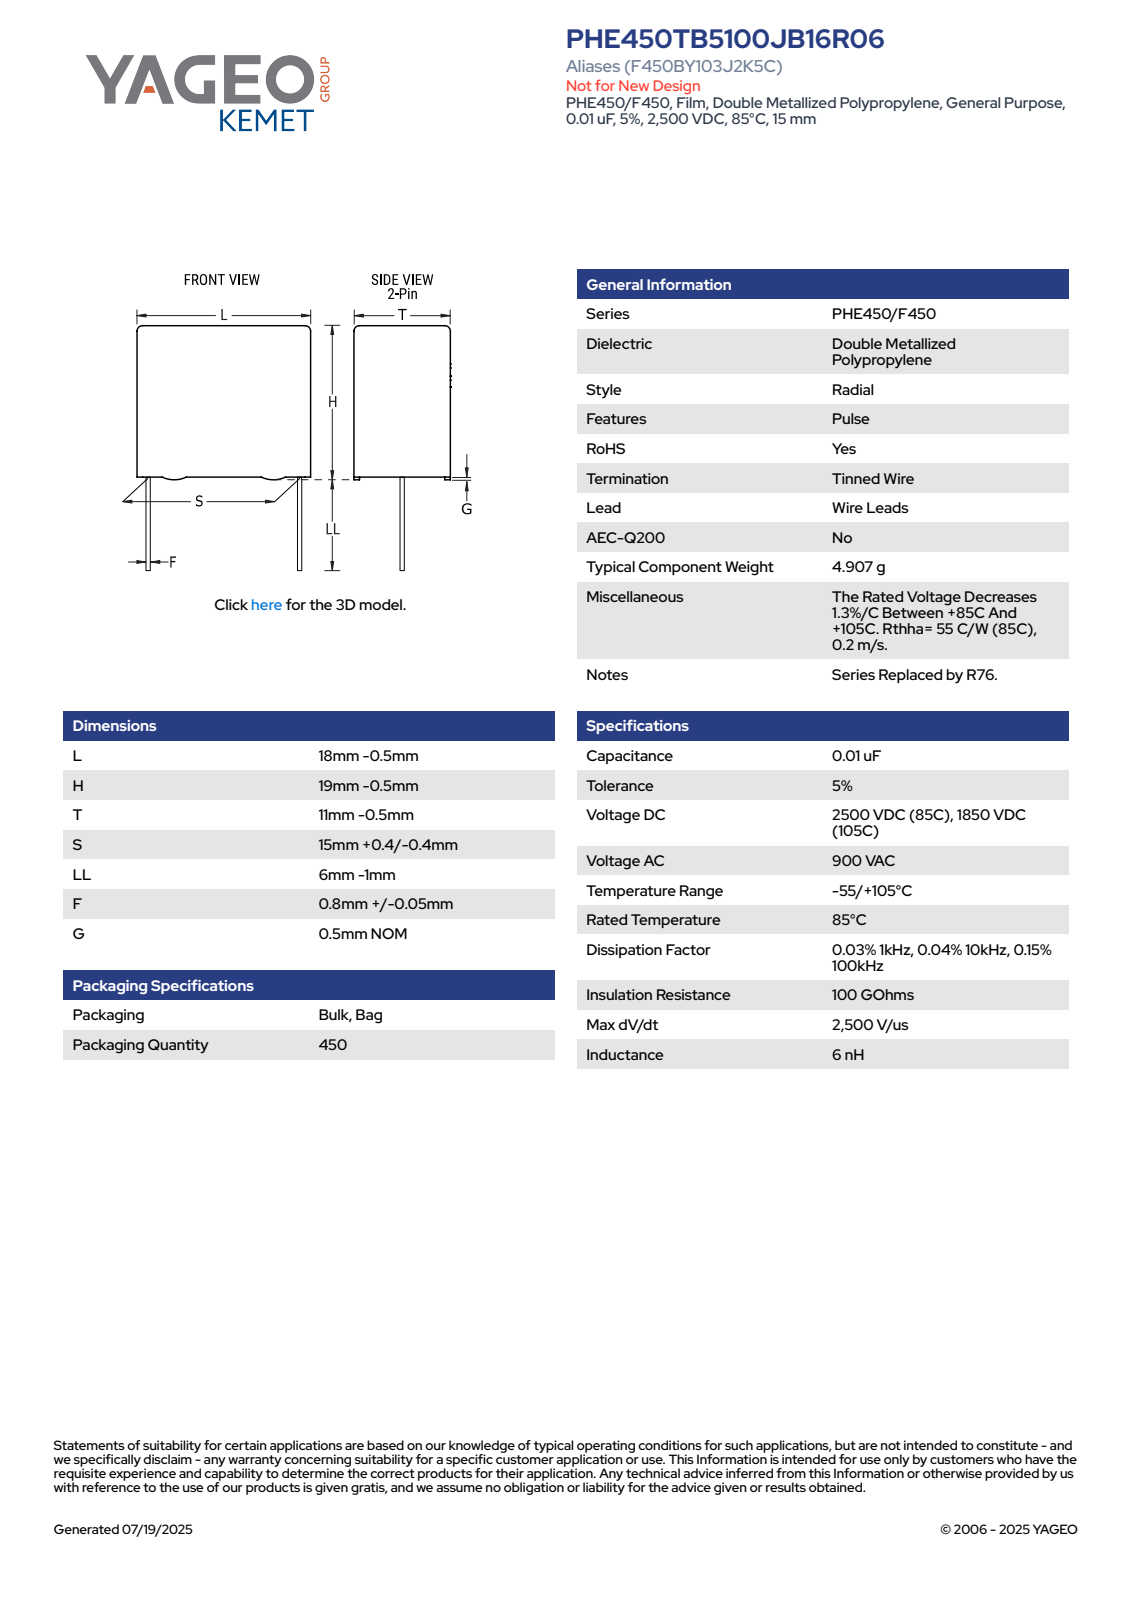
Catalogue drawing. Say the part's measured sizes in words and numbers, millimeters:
The part is named "CFR_RBG_18X19X11_L17.5H18.5T10.5S15LL5F0.85G0.5". Its 3-D file was written by "SolidWorks 2020 (AUTOMOTIVE_DESIGN)". It is 4 solids with 89 faces: 81 planar, 8 cylindrical and 0 other. Overall it measures 23.5 by 17.5 by 10.51 millimeters. Its volume is 3 314 cubic millimeters and its surface area 1 439 square millimeters. Round bosses or shafts: 2 of diameter 0.85. Partial cylindrical surfaces (rounded edges, fillets, slot ends): 4 of radius 0.5. The main face-to-face distances are 10.5, 17.5, 18, 10.51, 0.5, 18.5, 0.6, 9.9, 0.61, 9.3.
